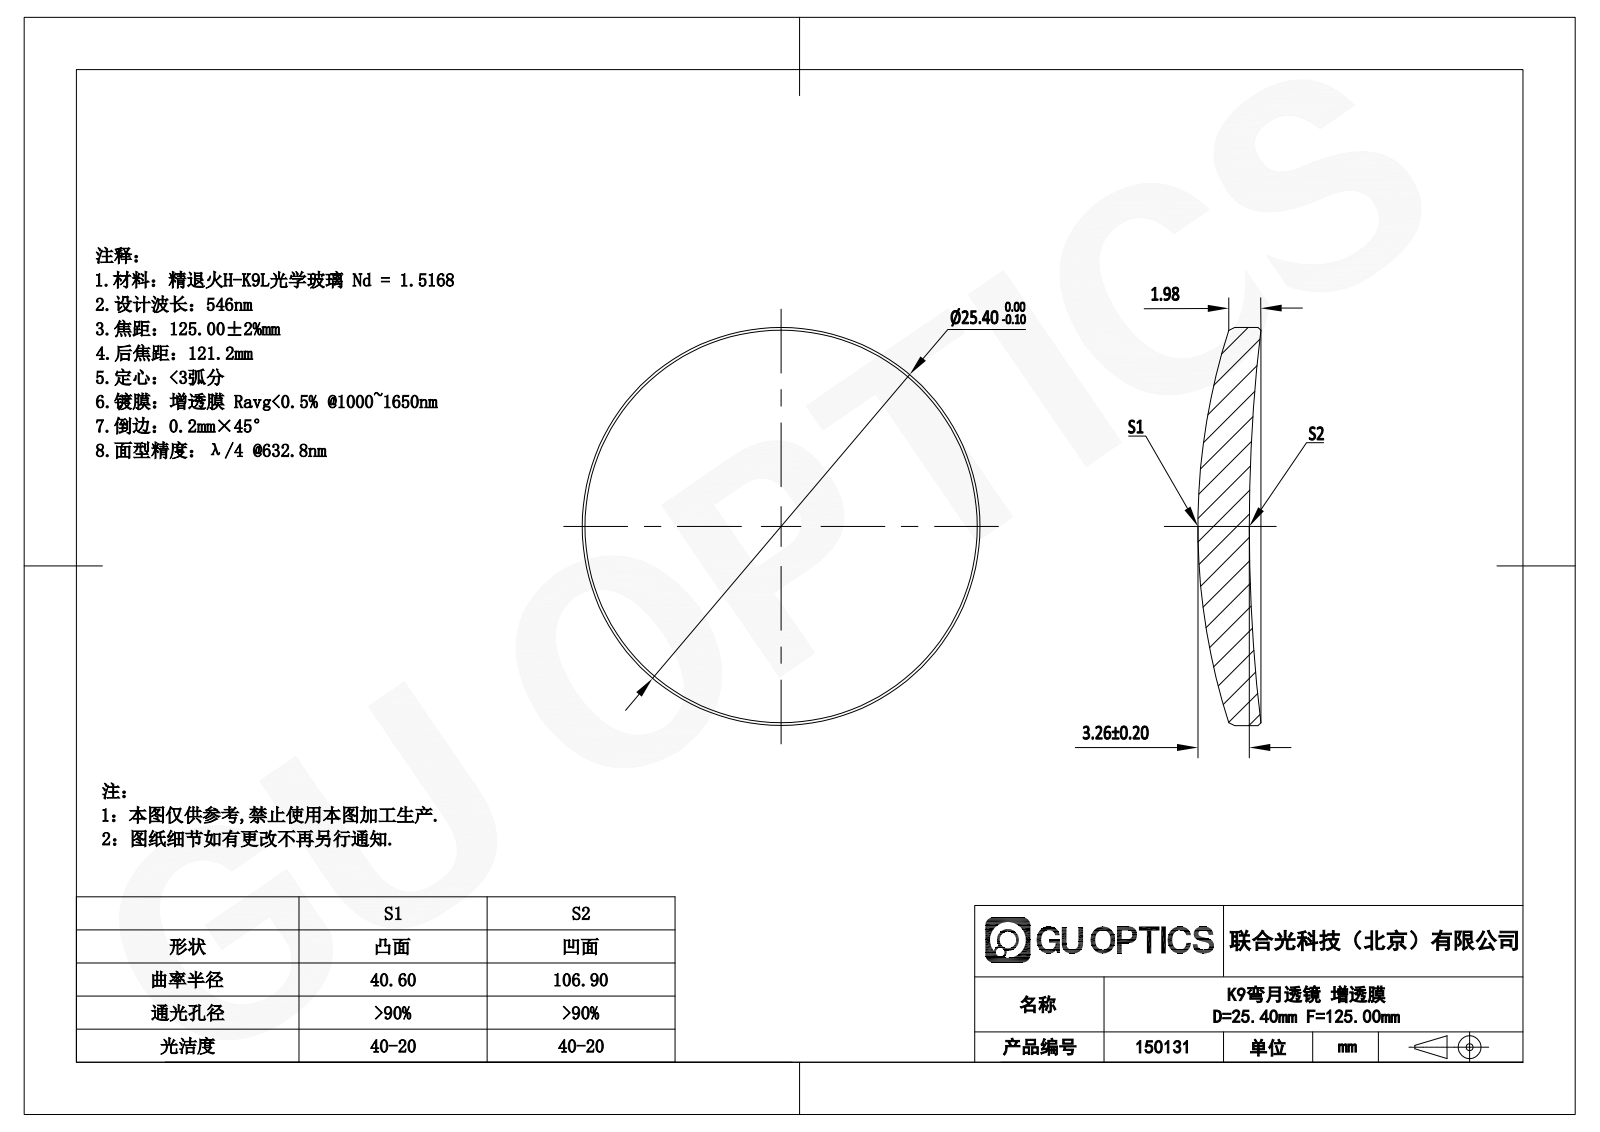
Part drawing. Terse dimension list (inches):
name: GLM1-025B-125-SWIR
written by: SolidWorks 2022 (AUTOMOTIVE_DESIGN)
unit: in
bodies: 1 solid, 10 faces (0 planar, 2 cylindrical, 8 other)
size: 1 × 1 × 0.158
volume: 0.082 in³; area: 1.814 in²
bosses: 1× ⌀1
